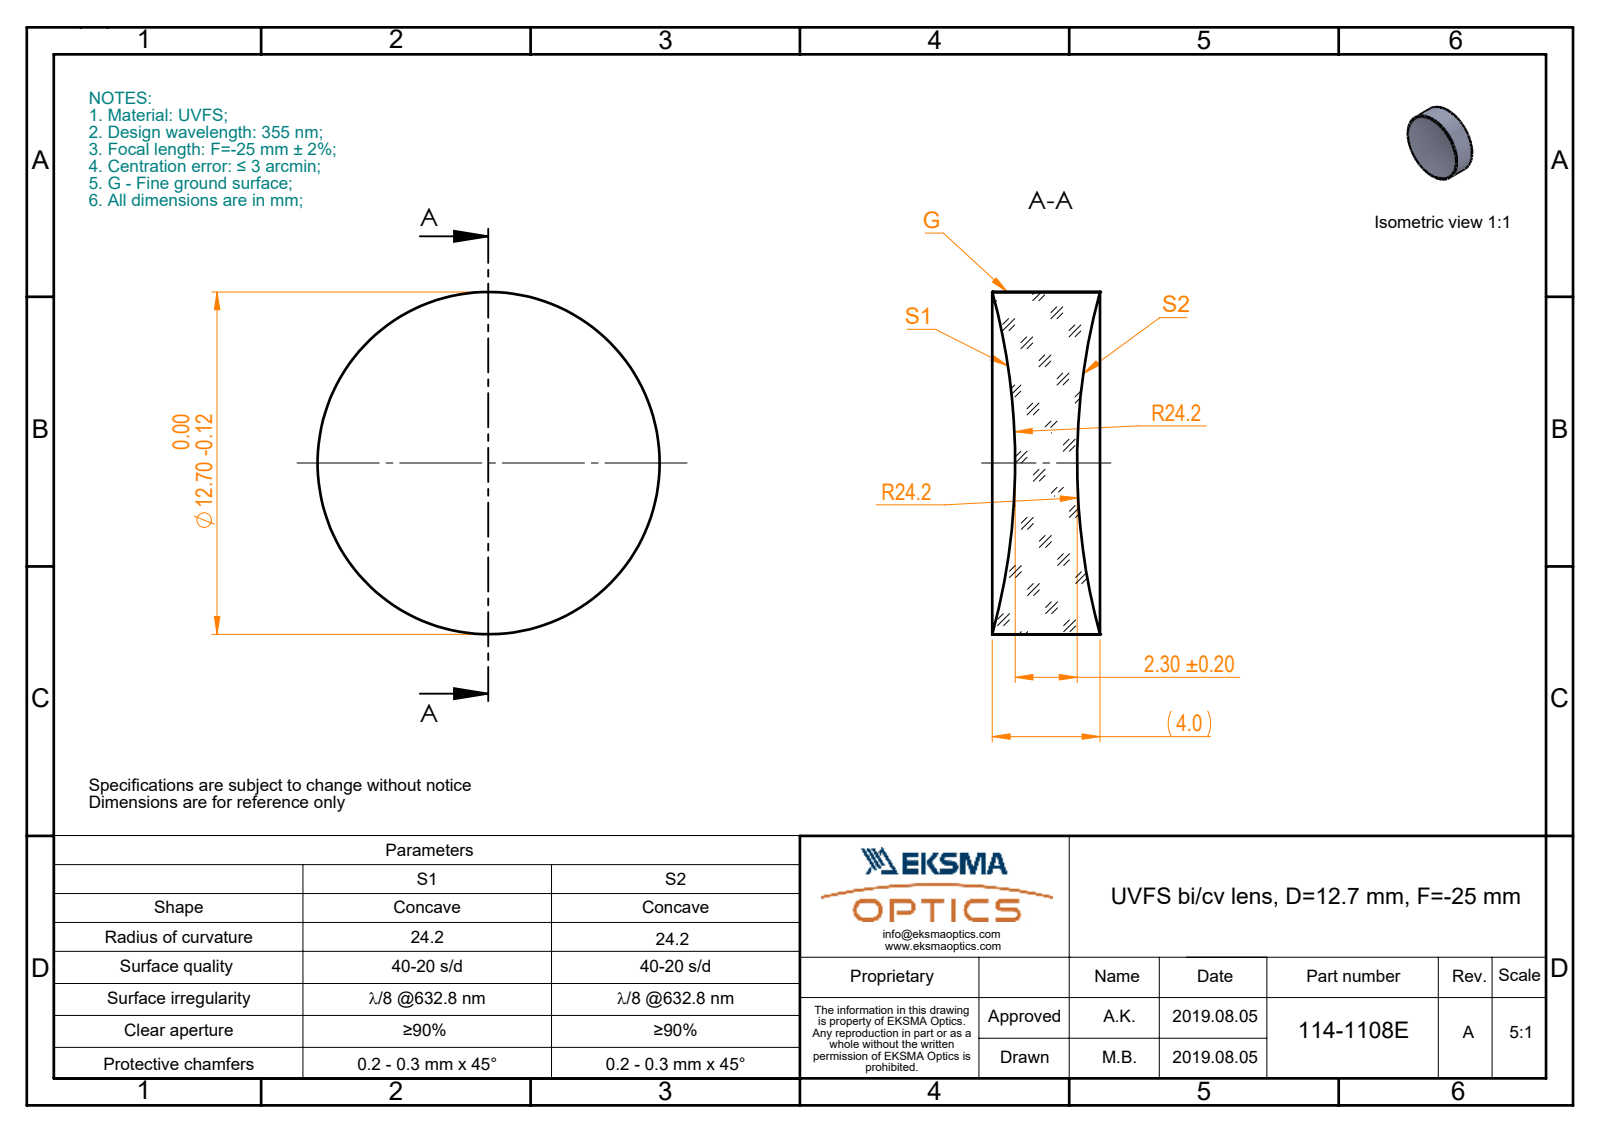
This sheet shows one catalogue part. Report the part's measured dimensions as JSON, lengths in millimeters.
{"part_name": "114-1108E UVFS bi-cv 12.7 F-25", "step_written_by": "SolidWorks 2017 (CONFIG_CONTROL_DESIGN)", "units": "millimeters", "bodies": {"solids": 1, "faces": 6, "planar": 0, "cylindrical": 2, "other": 4}, "overall_size": [12.7, 12.7, 4], "volume_mm3": 398, "surface_area_mm2": 417, "round_bosses_or_shafts": [[12.7, 1]]}
